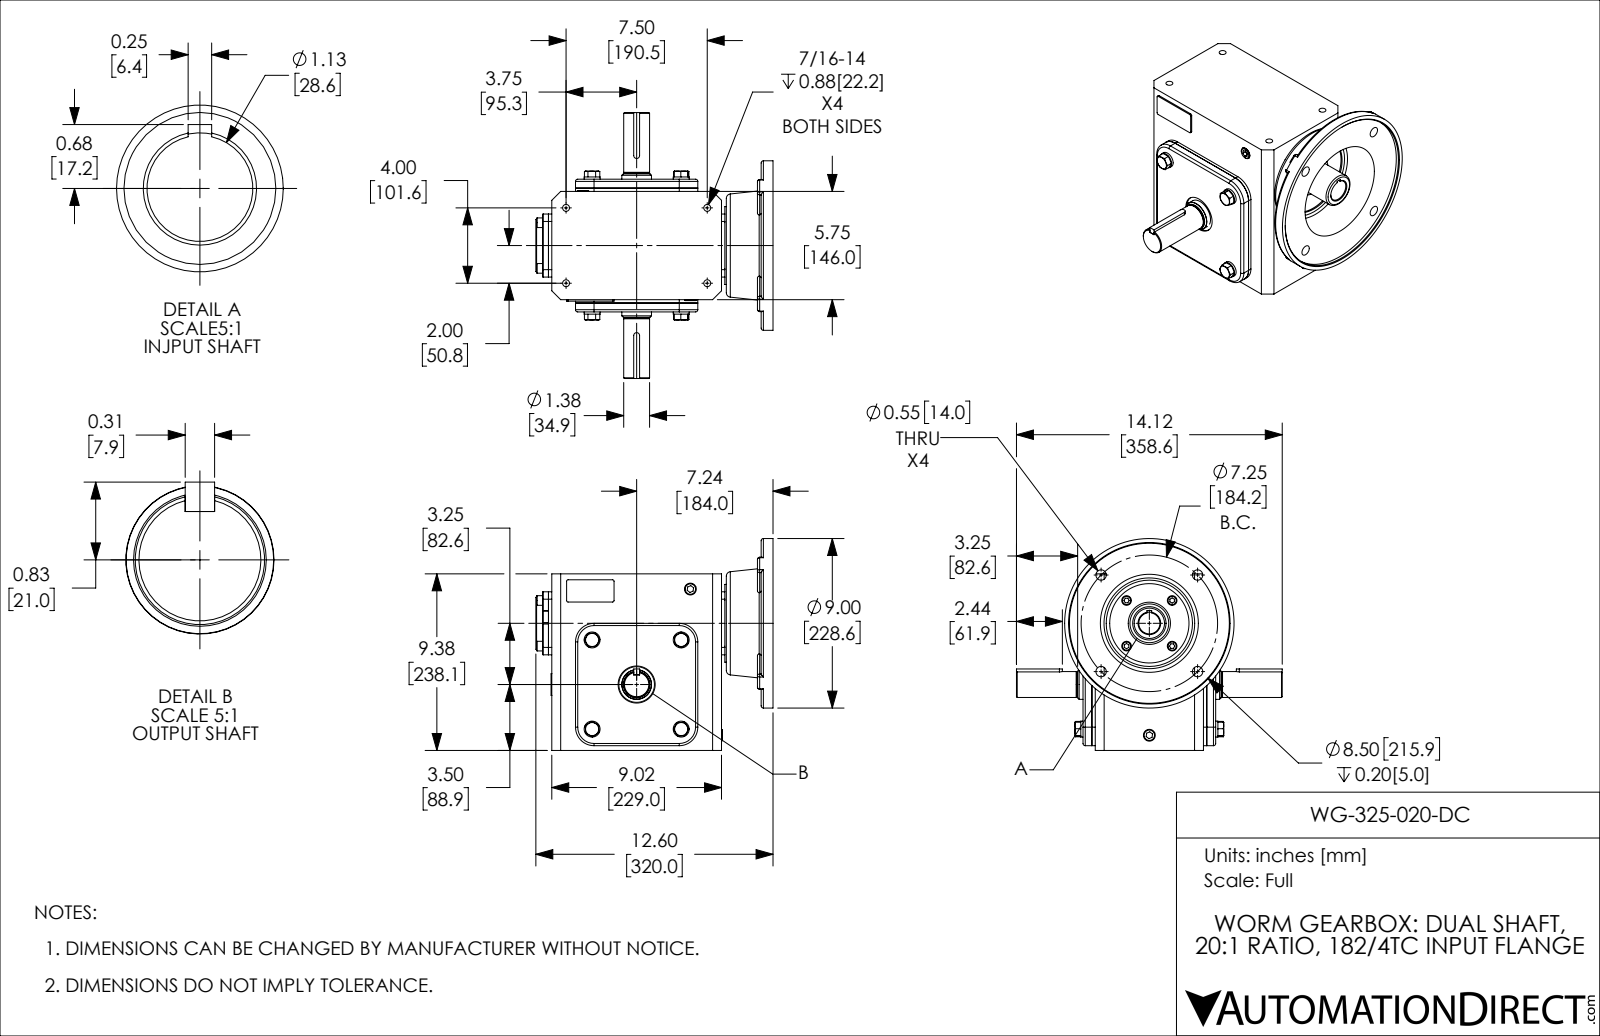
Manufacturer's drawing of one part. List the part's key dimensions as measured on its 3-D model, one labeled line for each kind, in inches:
Part name (STEP PRODUCT): WG-325-020-DC
STEP written by: SolidWorks 2017 (AUTOMOTIVE_DESIGN)
Units: inches
Bodies: 43 solids, 690 faces (349 planar, 206 cylindrical, 135 other)
Overall size (bounding box): 14.118 × 12.598 × 11.25
Volume: 542 in³ · Surface area: 1 065 in²
Round holes (diameter × count): ⌀0.354 ×4, ⌀0.368 ×4, ⌀0.551 ×4, ⌀0.628 ×3, ⌀0.591 ×1, ⌀0.978 ×1, ⌀1.125 ×1, ⌀1.181 ×1, ⌀1.969 ×1, ⌀2.244 ×1, ⌀2.441 ×1, ⌀2.756 ×1
Round bosses / shafts (diameter × count): ⌀0.846 ×4, ⌀0.512 ×4, ⌀9 ×1, ⌀4.134 ×1, ⌀2.835 ×1, ⌀1.772 ×1, ⌀1.575 ×1, ⌀1.375 ×1
Partial cylindrical surfaces — rounded edges, fillets, slot ends (radius × count): R0.118 ×18, R0.079 ×7, R0.394 ×4, R0.906 ×4, R0.984 ×4, R0.02 ×2, R0.039 ×2, R0.156 ×2
Main face-to-face distances: 0.079, 0.177, 6.496, 0.394, 6.969, 0.472, 6.575, 6.398, 0.571, 0.65
Hole centre spacings: 4.009, 1.713, 1.913, 2.422, 3.625, 5.127, 5.338, 2.372
